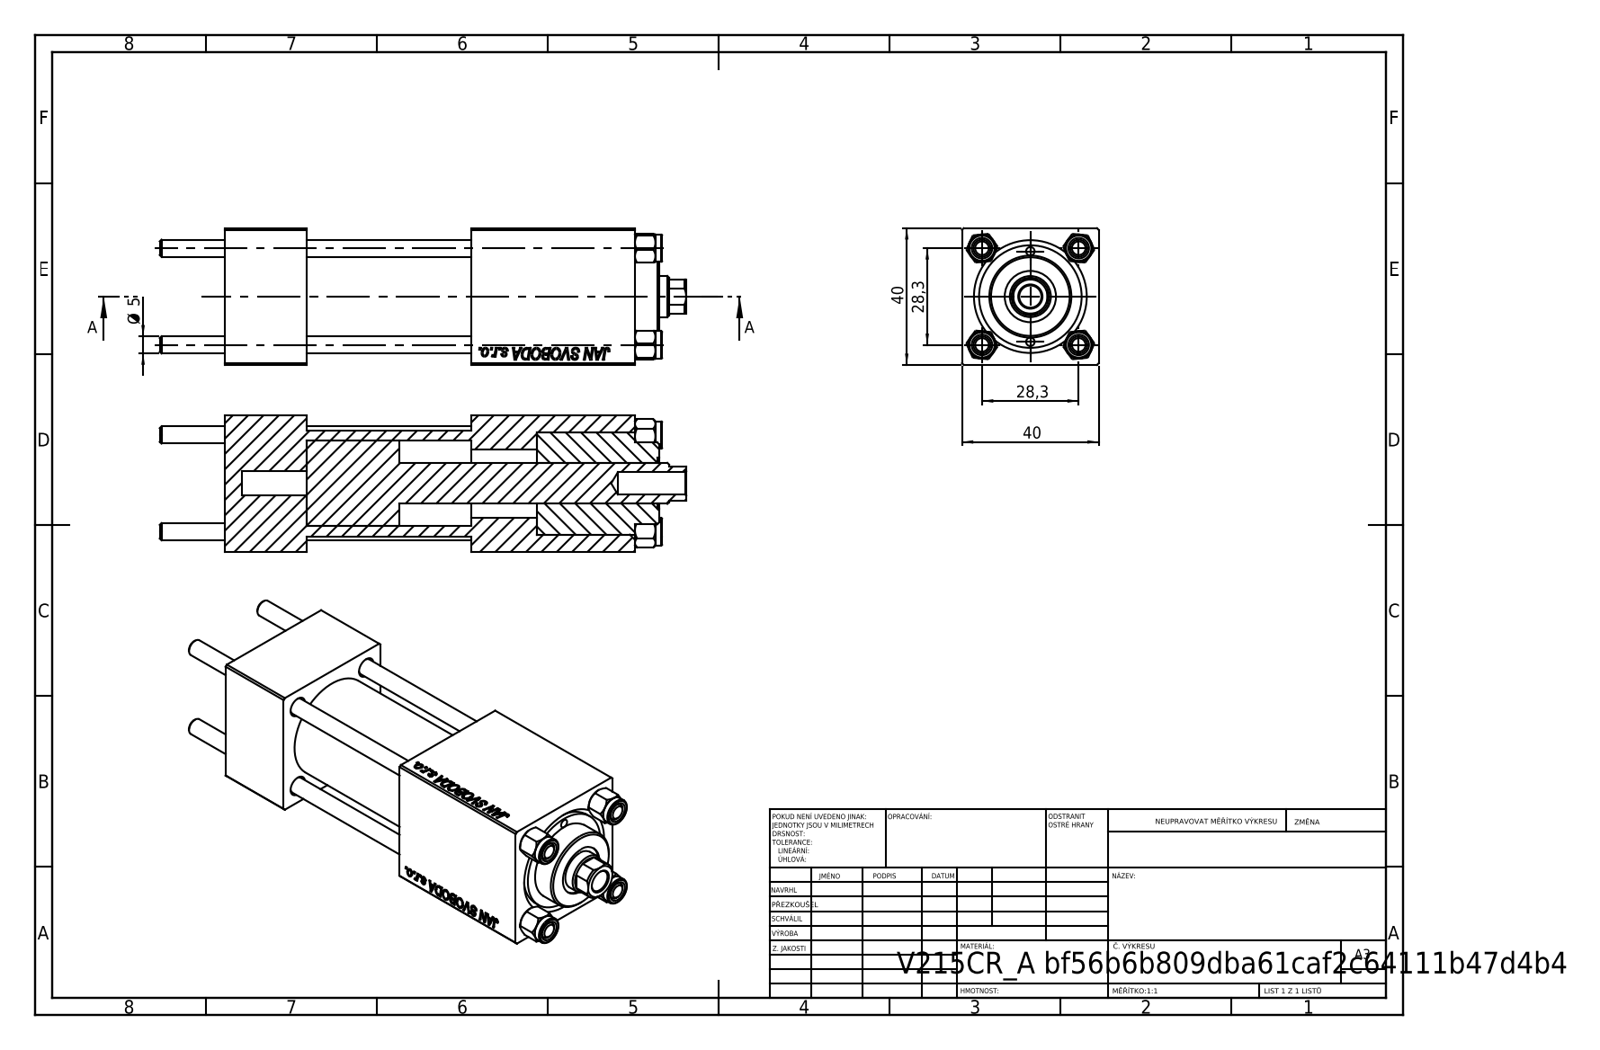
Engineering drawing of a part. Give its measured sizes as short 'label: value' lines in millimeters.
name: V215_VC_A; NUT_M5; V215CR_VCP; V215CR_BODY_A (+1 more)
written by: SolidWorks 2019 (CONFIG_CONTROL_DESIGN)
unit: mm
bodies: 11 solids, 1137 faces (519 planar, 82 cylindrical, 536 other)
size: 154 × 40 × 40
volume: 145 230 mm³; area: 59 227 mm²
holes: 4× ⌀5, 3× ⌀20, 2× ⌀2.5, 2× ⌀7, 2× ⌀13.16, 1× ⌀6.5, 1× ⌀12, 1× ⌀15, 1× ⌀25, 1× ⌀30
bosses: 4× ⌀8, 1× ⌀31, 1× ⌀24
rounds: 1× R5.5
face distances: 40, 48, 24, 91.3, 67.3, 120, 96, 28.7, 72, 19.3
hole spacings: 14.18, 20.01, 28.3, 30.84, 13.25, 40.02, 26.5, 73
